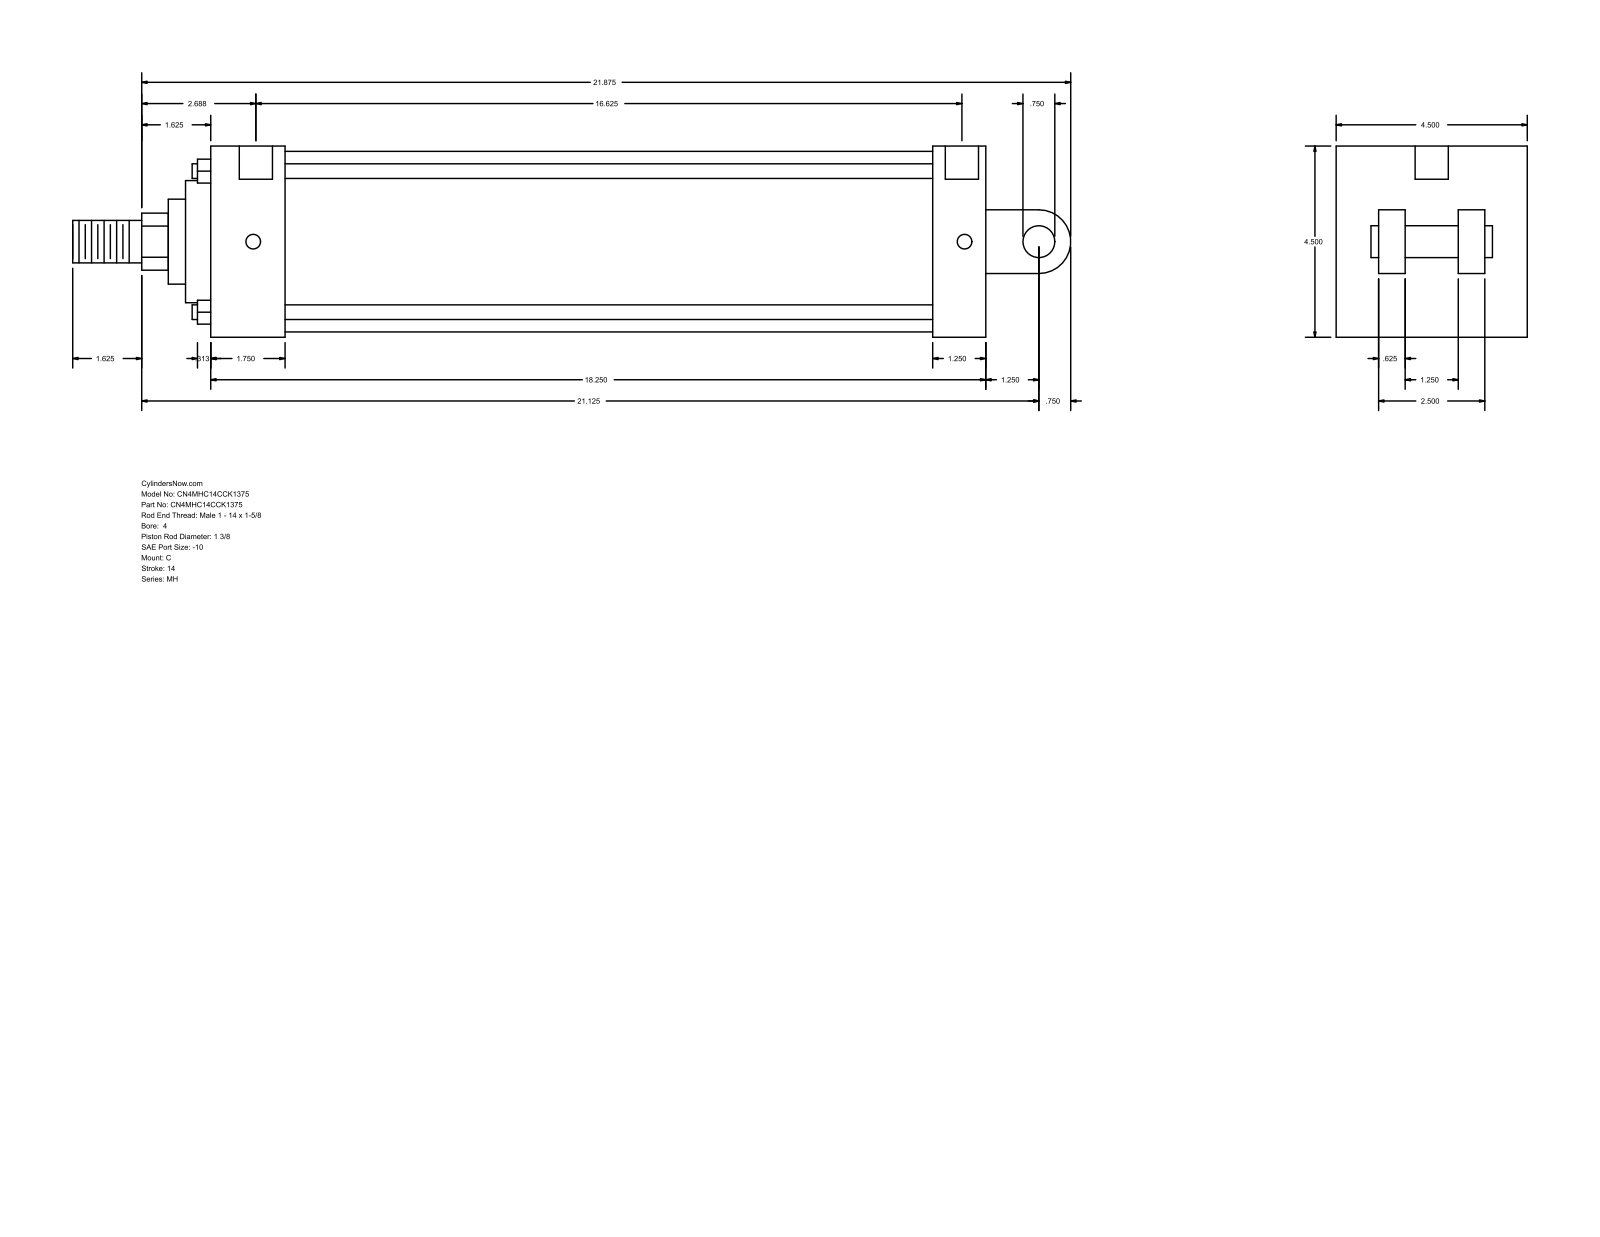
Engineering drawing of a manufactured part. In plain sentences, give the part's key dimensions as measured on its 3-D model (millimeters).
The part is named "MH_C__0400_1.375". Its 3-D file was written by "GSSL Pune (CONFIG_CONTROL_DESIGN)". It is 0 solids with 101 faces: 71 planar, 30 cylindrical and 0 other. Overall it measures 596.9 by 114.3 by 114.3 millimeters. Round holes: 4 of diameter 8.73, 2 of diameter 19.84. Round bosses or shafts: 4 of diameter 8.76, 1 of diameter 107.95, 1 of diameter 73.03, 1 of diameter 50.8, 1 of diameter 34.92, 1 of diameter 25.4, 1 of diameter 19.05. Partial cylindrical surfaces (rounded edges, fillets, slot ends): 1 of radius 17.06, 1 of radius 19.05. The main face-to-face distances are 114.3, 463.55, 44.45, 431.8, 387.35, 419.1, 31.75, 41.27, 73.03, 38.1. The hole center spacings are 425.45, 1.58, 1.59, 422.28, 423.86, 423.87.
